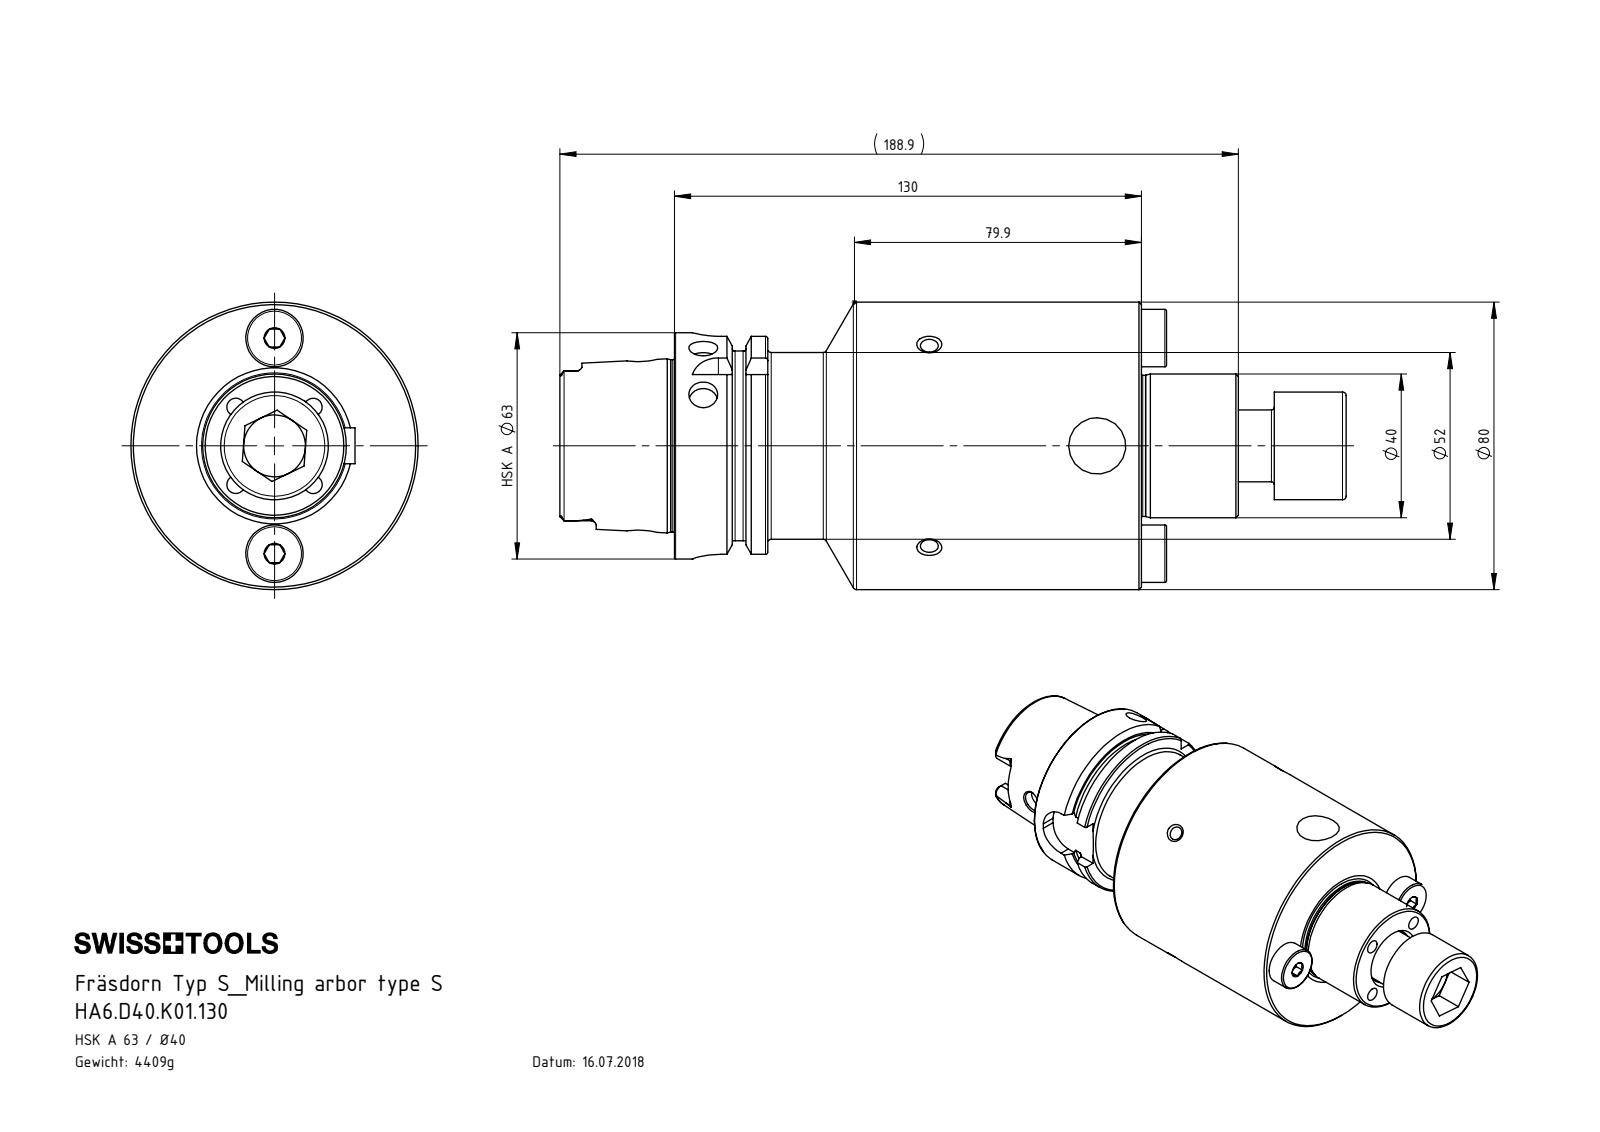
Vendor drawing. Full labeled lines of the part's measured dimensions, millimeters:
Part name (STEP PRODUCT): ISO 4762 - M20 x 40; DIN 6885 - 10x8x20; D40-ER2.001.023_B; HA6-D40.K01.130_C_Fertigbearbeitung (+1 more)
STEP written by: SolidWorks 2017 (AUTOMOTIVE_DESIGN)
Units: millimetres
Bodies: 5 solids, 393 faces (96 planar, 120 cylindrical, 177 other)
Overall size (bounding box): 218.9 × 80 × 80
Volume: 582 291 mm³ · Surface area: 74 358 mm²
Round holes (diameter × count): ⌀5 ×12, ⌀8 ×2, ⌀14 ×2, ⌀7.5 ×1, ⌀8.4 ×1, ⌀10 ×1, ⌀17 ×1, ⌀17.5 ×1, ⌀19 ×1, ⌀21 ×1, ⌀34 ×1, ⌀40 ×1
Round bosses / shafts (diameter × count): ⌀16 ×2, ⌀6 ×2, ⌀4.6 ×2, ⌀80 ×1, ⌀63 ×1, ⌀54.95 ×1, ⌀52 ×1, ⌀47.94 ×1
Partial cylindrical surfaces — rounded edges, fillets, slot ends (radius × count): R1.4 ×6, R2.88 ×4, R5 ×4, R8 ×4
Main face-to-face distances: 130, 30, 10, 157, 27, 20, 104.05, 16, 25.95, 131.05
Hole centre spacings: 15.25, 21.56, 22.04, 42.18, 48.05, 30, 30.49, 60
